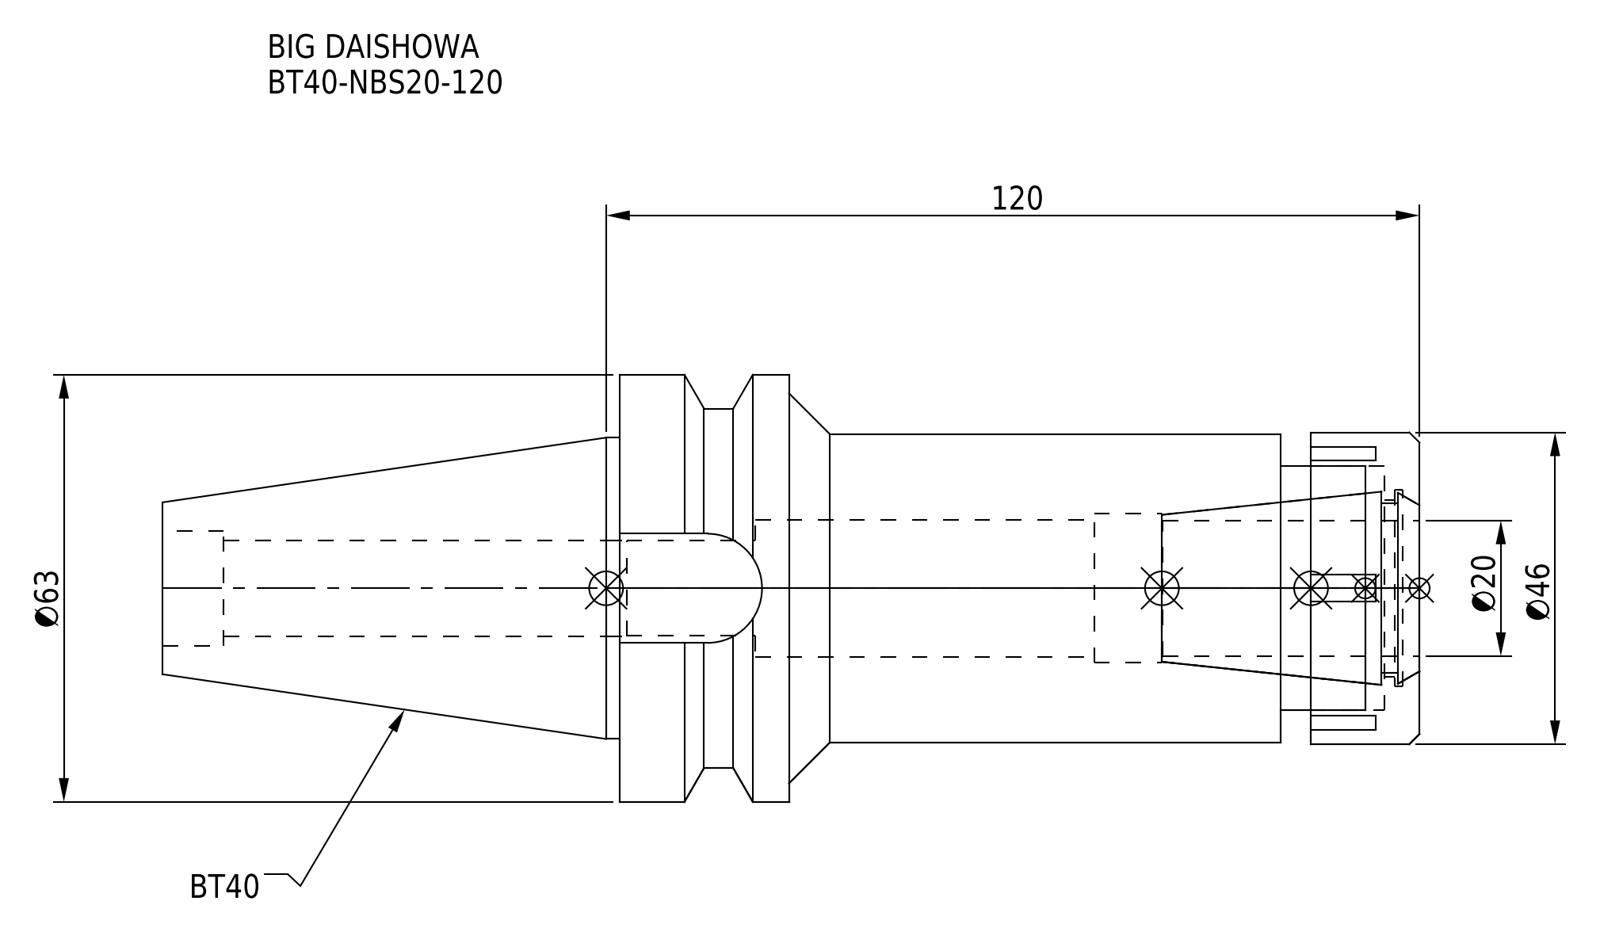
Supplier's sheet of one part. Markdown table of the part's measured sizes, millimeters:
| quantity | value |
| --- | --- |
| part name | BT40-NBS20-120.stp; BT40-NBS20-120_1.stp; BT40-NBS20-120-FreeParts; DXF_TEMP_ASSY_ASM_4_ASM.stp (+3 more) |
| STEP written by | SolidWorks 2019 (CONFIG_CONTROL_DESIGN) |
| units | millimeters |
| bodies | 2 solids, 93 faces (45 planar, 34 cylindrical, 14 other) |
| overall size | 185.4 × 63 × 63 |
| volume | 230 564 mm³ |
| surface area | 46 437 mm² |
| round holes (diameter × count) | 14 × 1, 14.2 × 1, 17 × 1, 20.3 × 1, 22 × 1, 26 × 1, 29 × 1, 36 × 1 |
| round bosses / shafts (diameter × count) | 63 × 1, 53 × 1, 46 × 1, 45.5 × 1, 44.45 × 1 |
| partial cylindrical surfaces (radius × count) | 8.05 × 1 |
| main face-to-face distances | 118, 8, 20.5, 97.5, 16, 4.5, 102, 93, 77, 72.5 |
